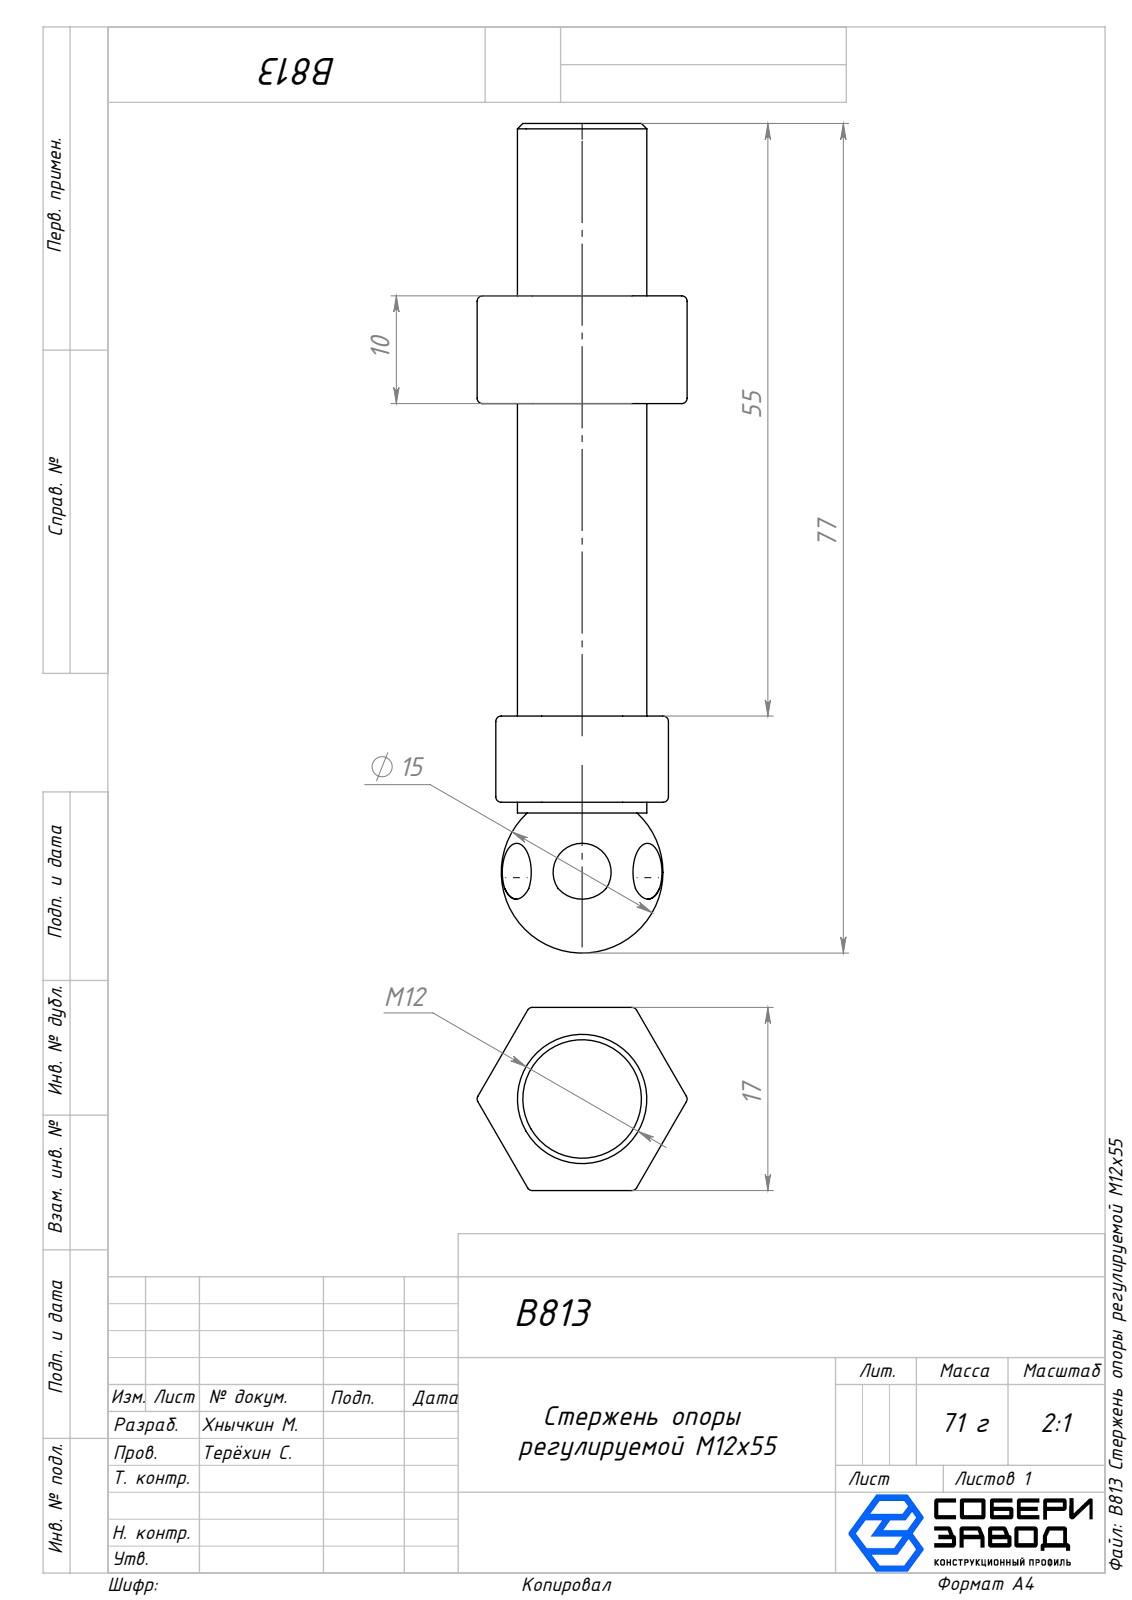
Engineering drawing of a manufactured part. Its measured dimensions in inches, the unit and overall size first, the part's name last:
Units: inches
Overall size (bounding box): 3.031 × 0.767 × 0.669
Round holes (diameter × count): ⌀0.394 ×1
Round bosses / shafts (diameter × count): ⌀0.472 ×1
Partial cylindrical surfaces — rounded edges, fillets, slot ends (radius × count): R0.02 ×36, R0.118 ×3
Main face-to-face distances: 0.059, 0.61, 0.669, 0.551, 0.394, 1.024, 0.63, 1.457, 1.85, 2.48
Volume: 0.673 in³ · Surface area: 7.025 in²
Bodies: 2 solids, 104 faces (24 planar, 48 cylindrical, 32 other)
Part name (STEP PRODUCT): Стержень_00; Гайка_00; B813 Стержень опоры регулируемой М12х55
STEP written by: SolidWorks 2025 (AUTOMOTIVE_DESIGN)
